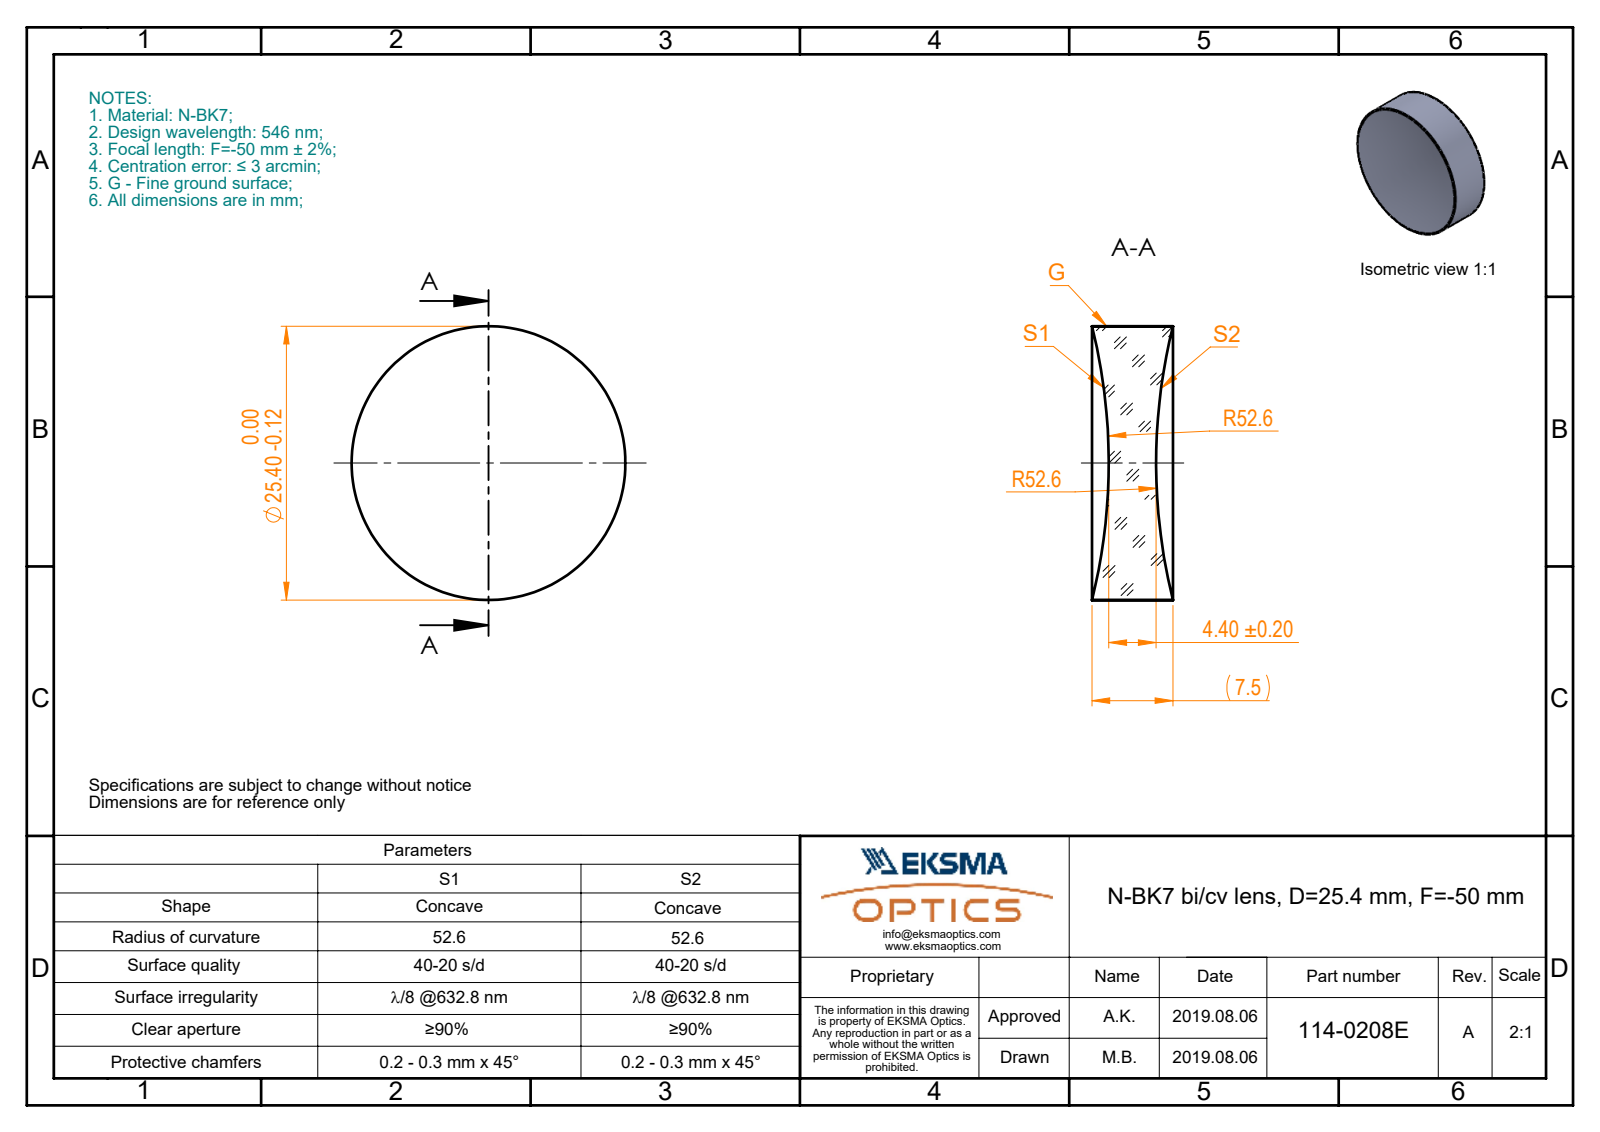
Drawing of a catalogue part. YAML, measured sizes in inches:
part_name: "114-0208E BK7 bi-cv 25.4 F-50"
step_written_by: "SolidWorks 2017 (CONFIG_CONTROL_DESIGN)"
units: inches
bodies: {solids: 1, faces: 6, planar: 0, cylindrical: 2, other: 4}
overall_size: [1, 1, 0.296]
volume: 0.184
surface_area: 2.523
round_bosses_or_shafts:
  - {diameter: 1, count: 1}
